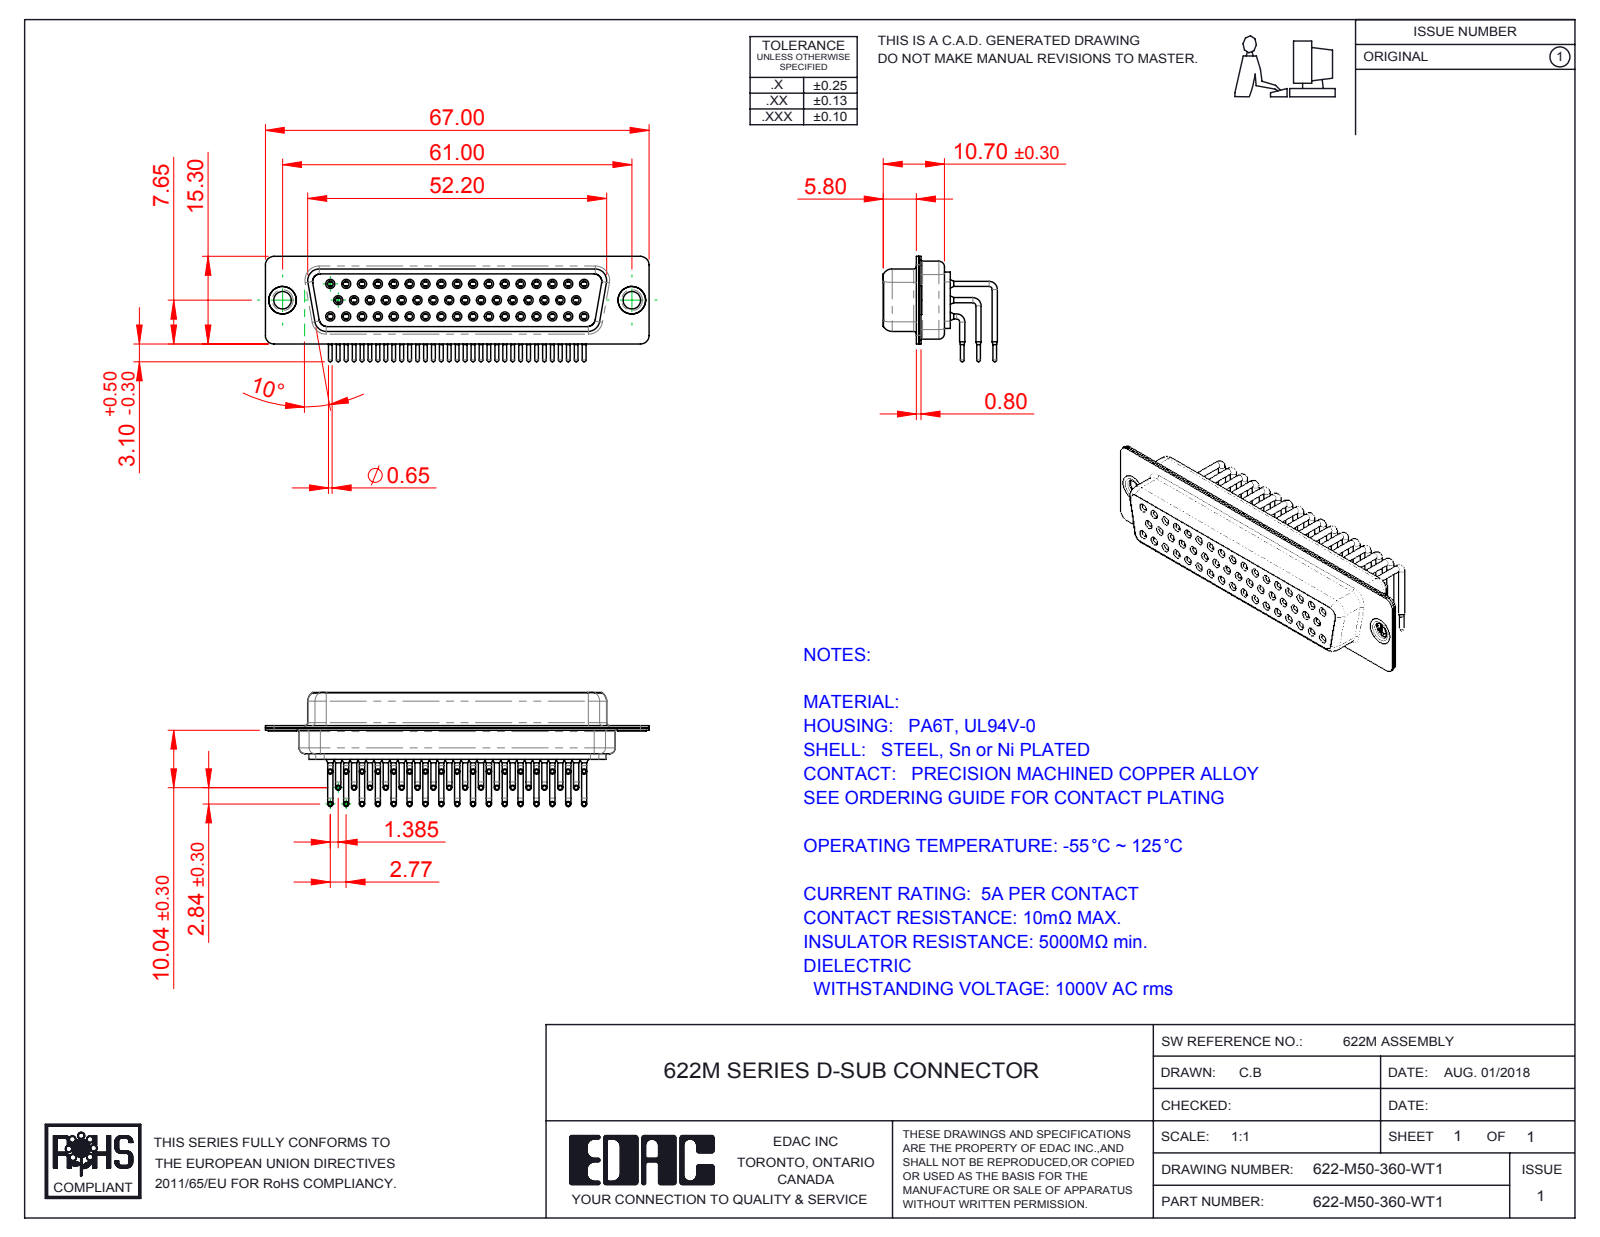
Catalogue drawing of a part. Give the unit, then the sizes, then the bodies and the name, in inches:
Units: inches
Overall size (bounding box): 2.638 × 0.785 × 0.724
Round holes (diameter × count): ⌀0.039 ×50, ⌀0.043 ×50, ⌀0.067 ×50, ⌀0.071 ×50, ⌀0.079 ×50, ⌀0.12 ×2, ⌀0.157 ×2, ⌀0.189 ×2
Round bosses / shafts (diameter × count): ⌀0.035 ×100, ⌀0.063 ×50, ⌀0.059 ×50, ⌀0.026 ×50, ⌀0.197 ×2, ⌀0.193 ×2, ⌀0.14 ×2
Partial cylindrical surfaces — rounded edges, fillets, slot ends (radius × count): R0.059 ×16, R0.079 ×12, R0.053 ×8, R0.063 ×8, R0.01 ×4, R0.02 ×4, R0.024 ×4, R0.026 ×4
Main face-to-face distances: 0.016, 0.053, 0.467, 0.033, 0.087, 0.217, 0.482, 0.232, 0.413, 0.396
Hole centre spacings: 0.109, 0.124, 0.218, 0.327, 0.436, 0.545, 0.654, 0.763
Volume: 0.418 in³ · Surface area: 24.77 in²
Bodies: 55 solids, 2903 faces (817 planar, 1271 cylindrical, 815 other)
Part name (STEP PRODUCT): 622M Housing_50 Contacts; 622M Shell Rear_50 Contacts; 622-M50-360-WT1; 622M Contact Row 3 (+4 more)
STEP written by: SolidWorks 2016 (CONFIG_CONTROL_DESIGN)
